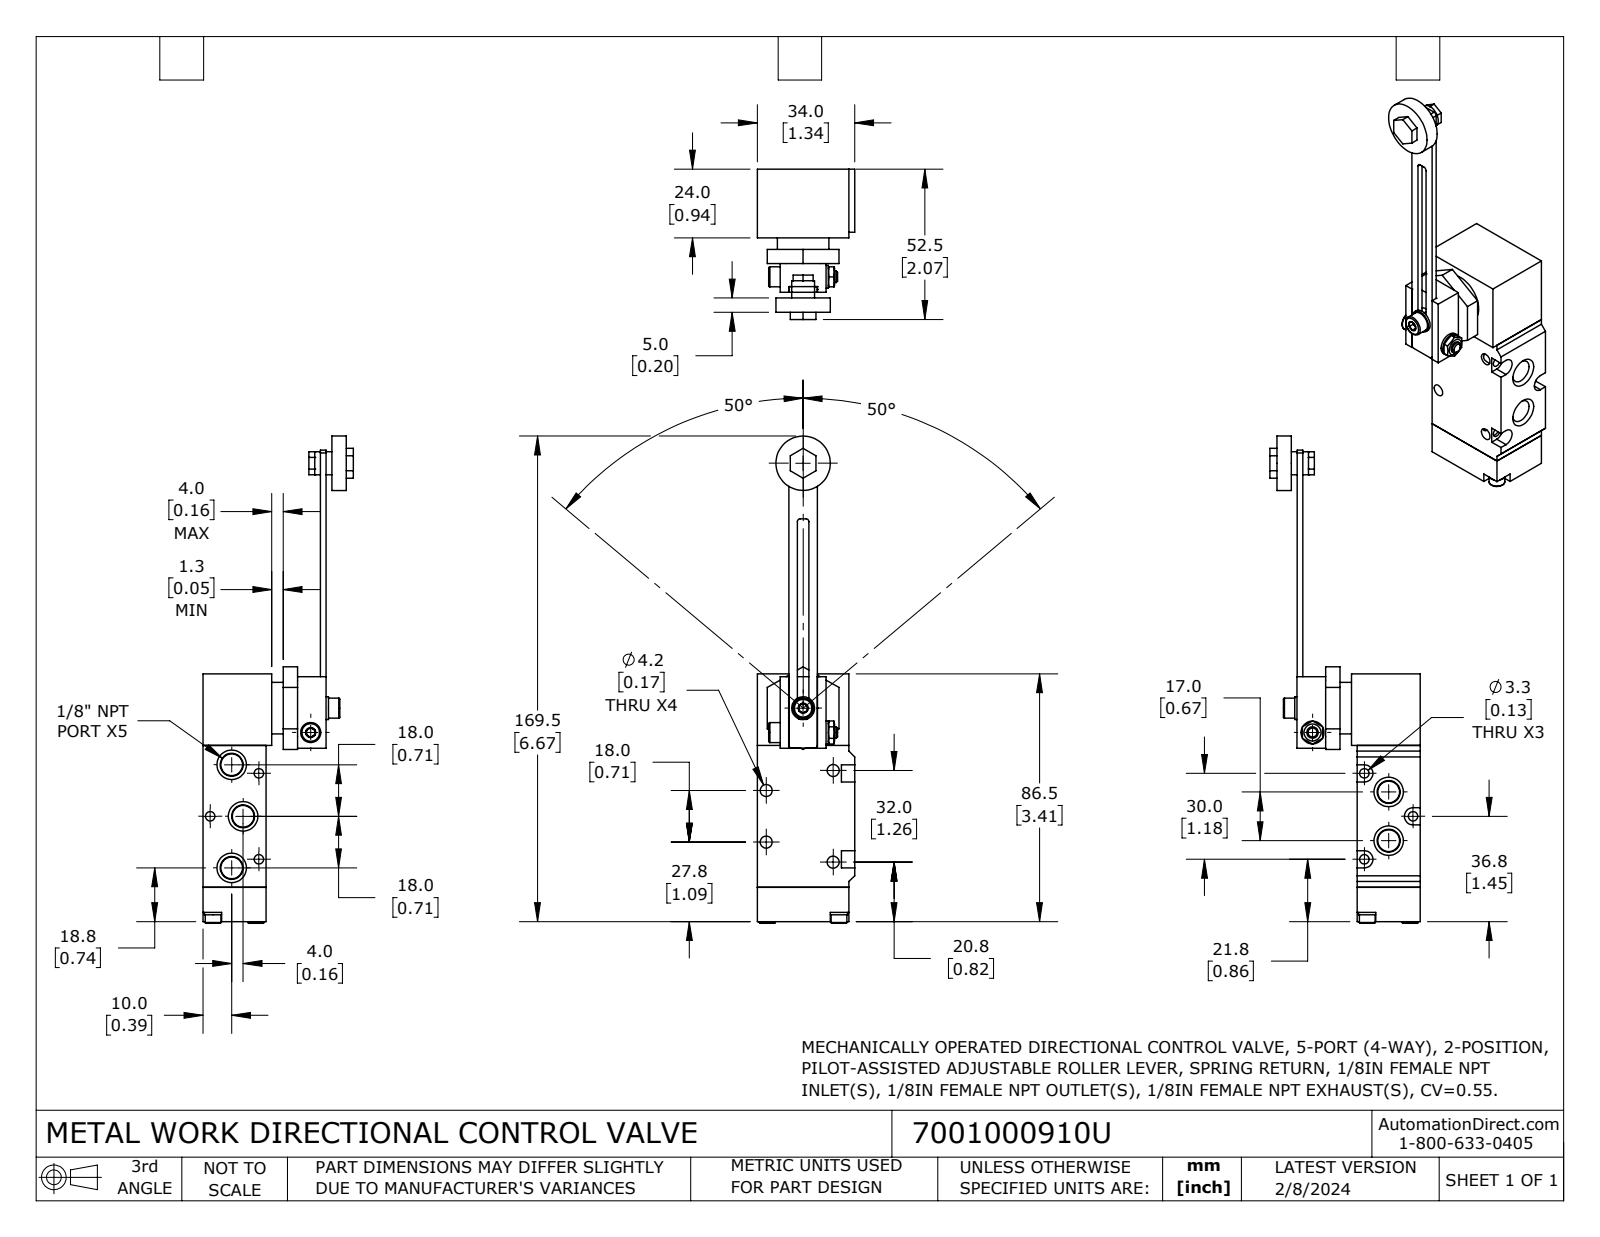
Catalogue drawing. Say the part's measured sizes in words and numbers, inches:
The part is named "7001000910U". Its 3-D file was written by "SolidWorks 2023 (CONFIG_CONTROL_DESIGN)". It is 14 solids with 344 faces: 178 planar, 82 cylindrical and 84 other. Overall it measures 6.697 by 2.067 by 1.339 inches. Its volume is 4.331 cubic inches and its surface area 38.96 square inches. Round holes: 5 of diameter 0.165, 3 of diameter 0.13, 3 of diameter 0.157, 2 of diameter 0.118, 1 of diameter 0.128, 1 of diameter 0.315. Round bosses or shafts: 2 of diameter 0.315, 2 of diameter 0.276, 2 of diameter 0.236, 2 of diameter 0.217, 1 of diameter 0.748, 1 of diameter 0.709. Partial cylindrical surfaces (rounded edges, fillets, slot ends): 8 of radius 0.039, 3 of radius 0.118, 1 of radius 0.004. The main face-to-face distances are 0.866, 0.079, 1.949, 0.315, 0.433, 0.945, 0.984, 0.826, 0.748, 0.512. The hole center spacings are 0.893, 0.961, 1.348, 0.709, 0.907, 0.951, 1.148, 1.181.
